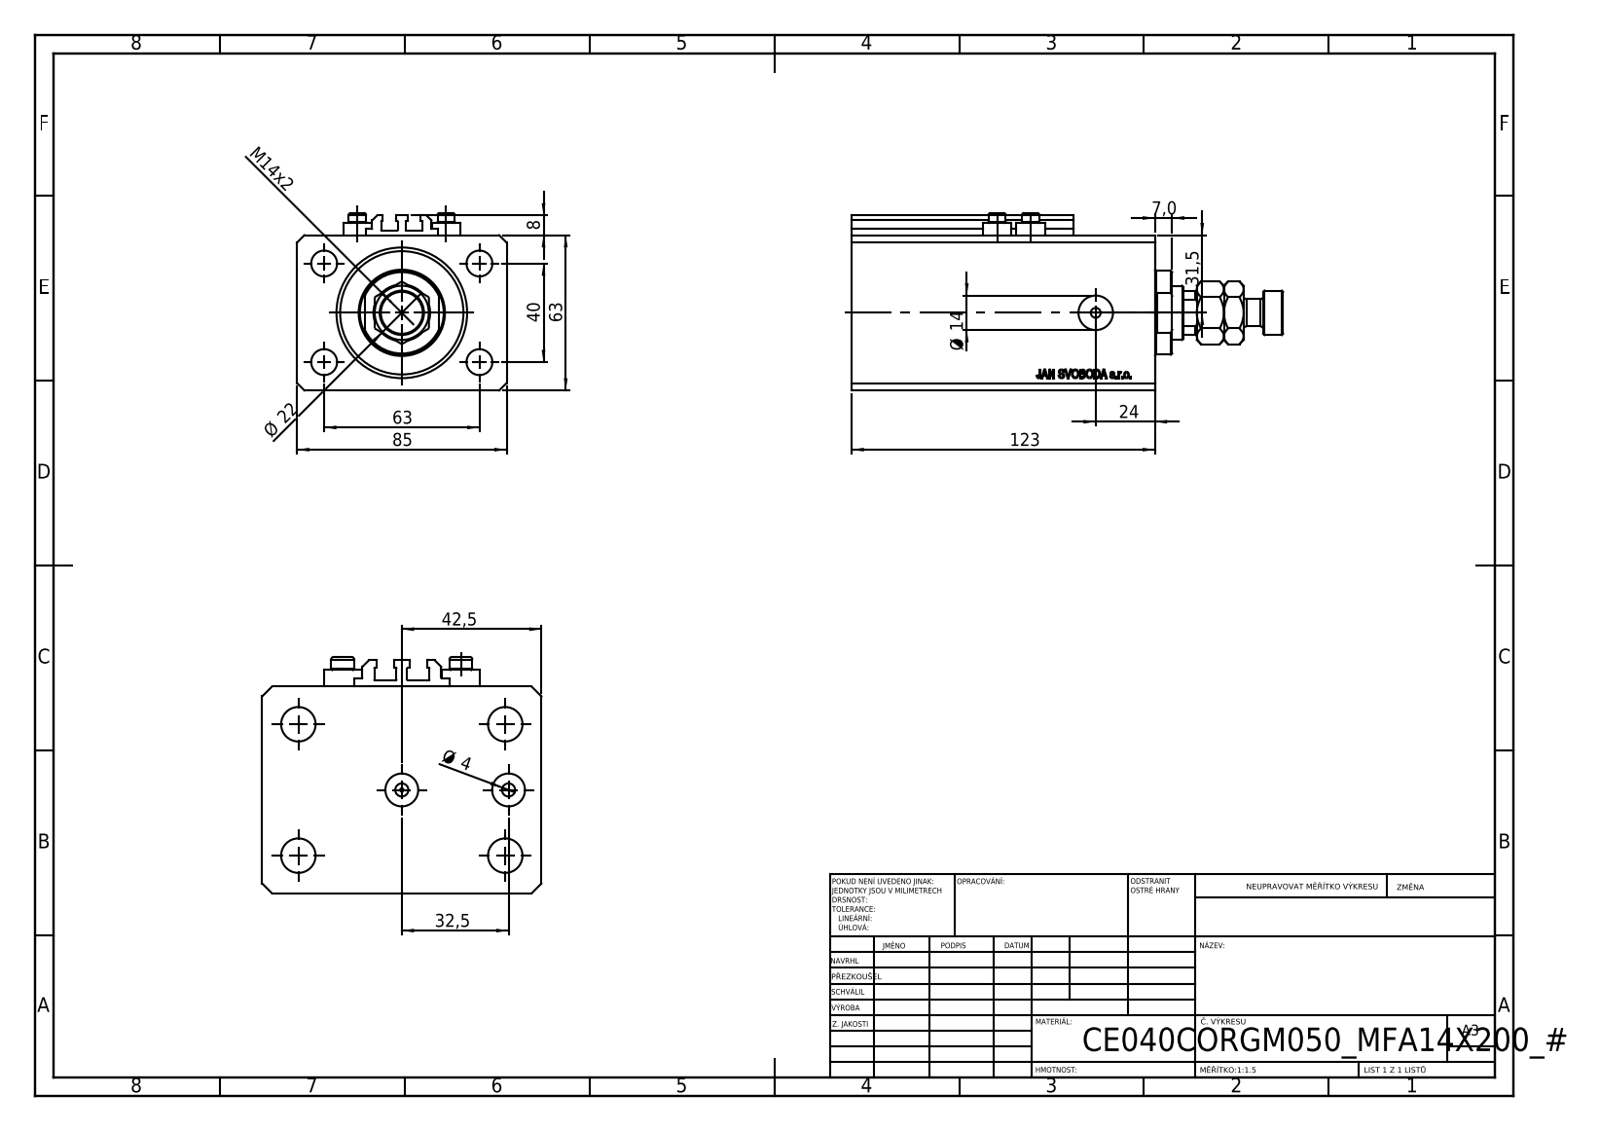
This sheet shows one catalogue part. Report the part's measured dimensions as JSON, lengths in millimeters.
{"part_name": "V250CE_C_Body; V250CE_C_VCP; MFA; ALLEN BOLT V250CE (+1 more)", "step_written_by": "SolidWorks 2019 (CONFIG_CONTROL_DESIGN)", "units": "millimeters", "bodies": {"solids": 9, "faces": 1090, "planar": 520, "cylindrical": 92, "other": 478}, "overall_size": [175, 85, 72], "volume_mm3": 597546, "surface_area_mm2": 117415, "round_holes": [[4, 8], [10.5, 4], [10, 2], [14, 2], [1.25, 1], [12.5, 1], [22, 1], [40, 1], [53, 1]], "round_bosses_or_shafts": [[11.6, 4], [7, 4], [34, 1], [18, 1], [11, 1]], "partial_cylinders_radius": [[0.2, 10], [10.5, 1]], "face_to_face_distances": [63, 85, 123, 17, 106, 11.4, 94.6, 111.6, 10, 2.5], "hole_center_spacings": [37.31, 13.6, 20.02, 36, 38.48, 40, 63, 67.05]}
